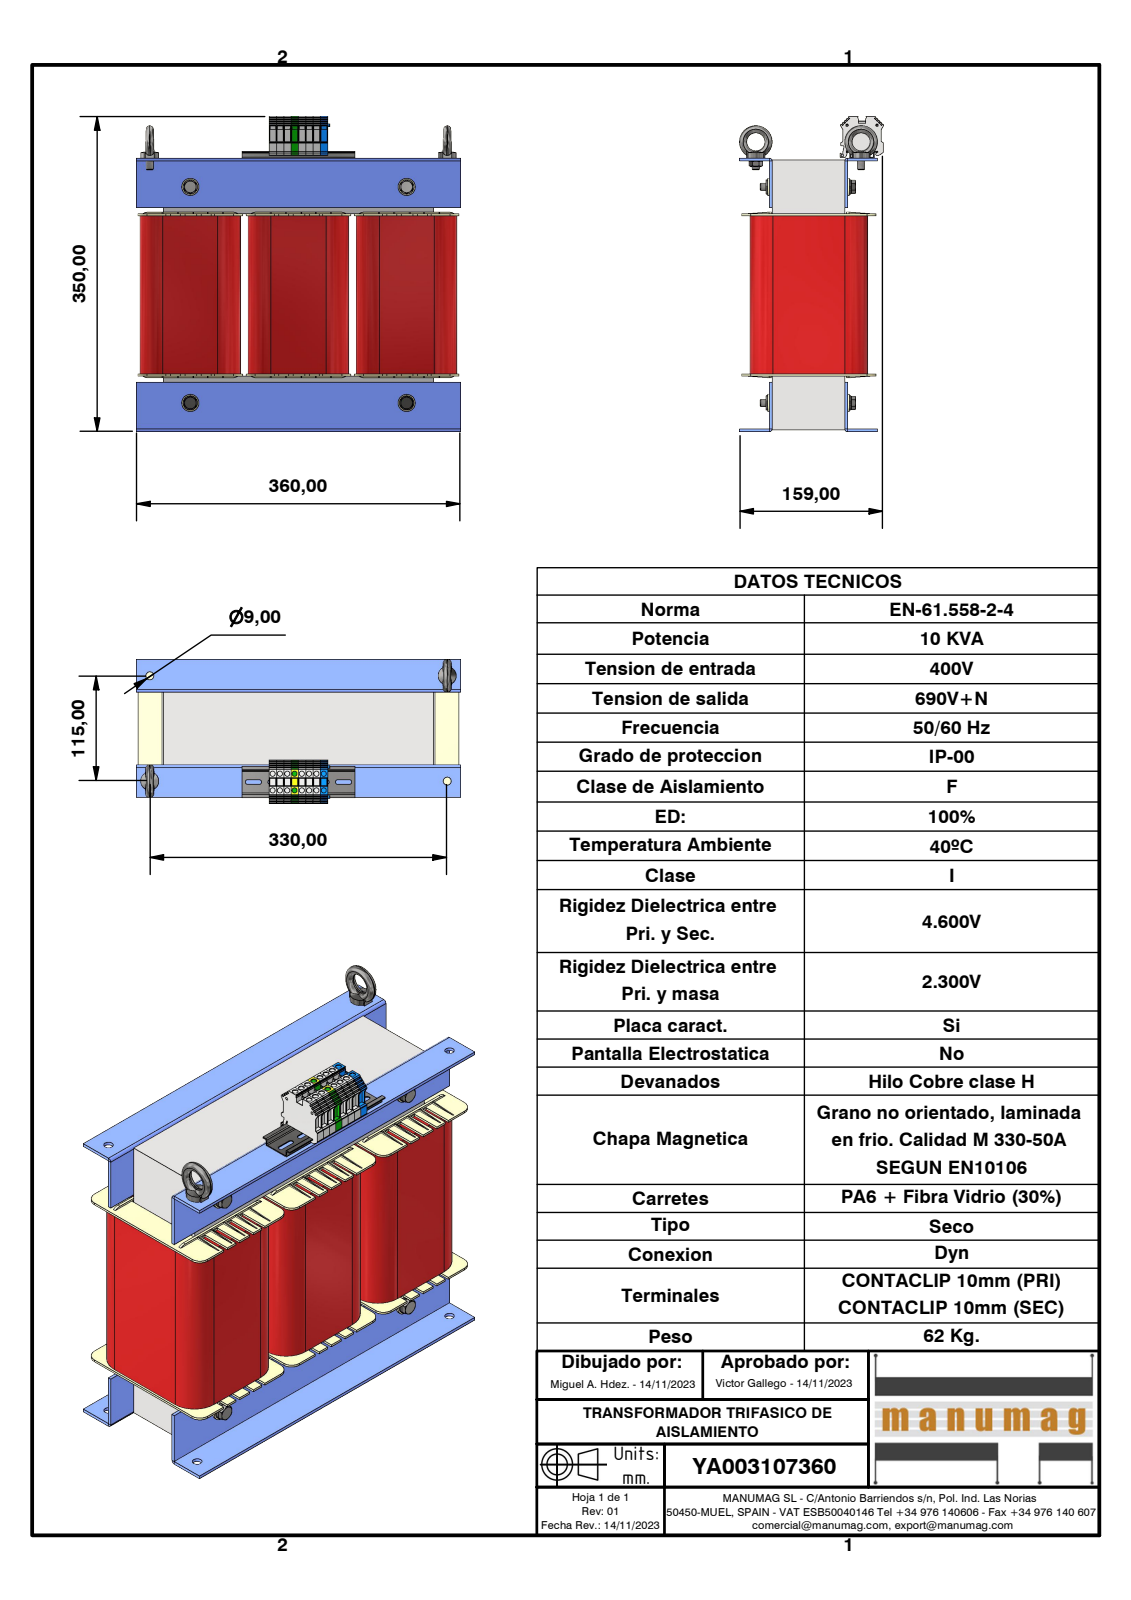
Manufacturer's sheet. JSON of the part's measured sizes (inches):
{"part_name": "YA003107360; UI 180 - 80 (300x300); UI 180_80_BOBINADO; RC60 NT060 (+8 more)", "step_written_by": "Autodesk Inventor 2023 (AUTOMOTIVE_DESIGN)", "units": "inches", "bodies": {"solids": 40, "faces": 3319, "planar": 2358, "cylindrical": 793, "other": 168}, "overall_size": [14.173, 13.799, 6.257], "volume_in3": 645, "surface_area_in2": 2310, "round_holes": [[0.224, 16], [0.315, 4], [0.331, 4], [0.354, 4], [0.413, 4], [0.433, 4], [0.094, 2], [0.098, 2], [0.108, 2], [0.787, 2], [0.262, 1]], "round_bosses_or_shafts": [[0.748, 4], [0.63, 4], [0.449, 4], [0.378, 4], [0.288, 4], [1.417, 2], [0.315, 2], [0.276, 2]], "partial_cylinders_radius": [[0.012, 81], [0.039, 28], [0.394, 26], [0.079, 17], [0.118, 12], [0.13, 12], [0.999, 12], [0.102, 10]], "face_to_face_distances": [0.039, 0.079, 0.118, 3.268, 4.724, 2.362, 0.881, 0.92, 3.15, 9.449], "hole_center_spacings": [0.319, 0.791, 0.638, 0.965, 0.957, 1.2, 0.724, 1.276]}
